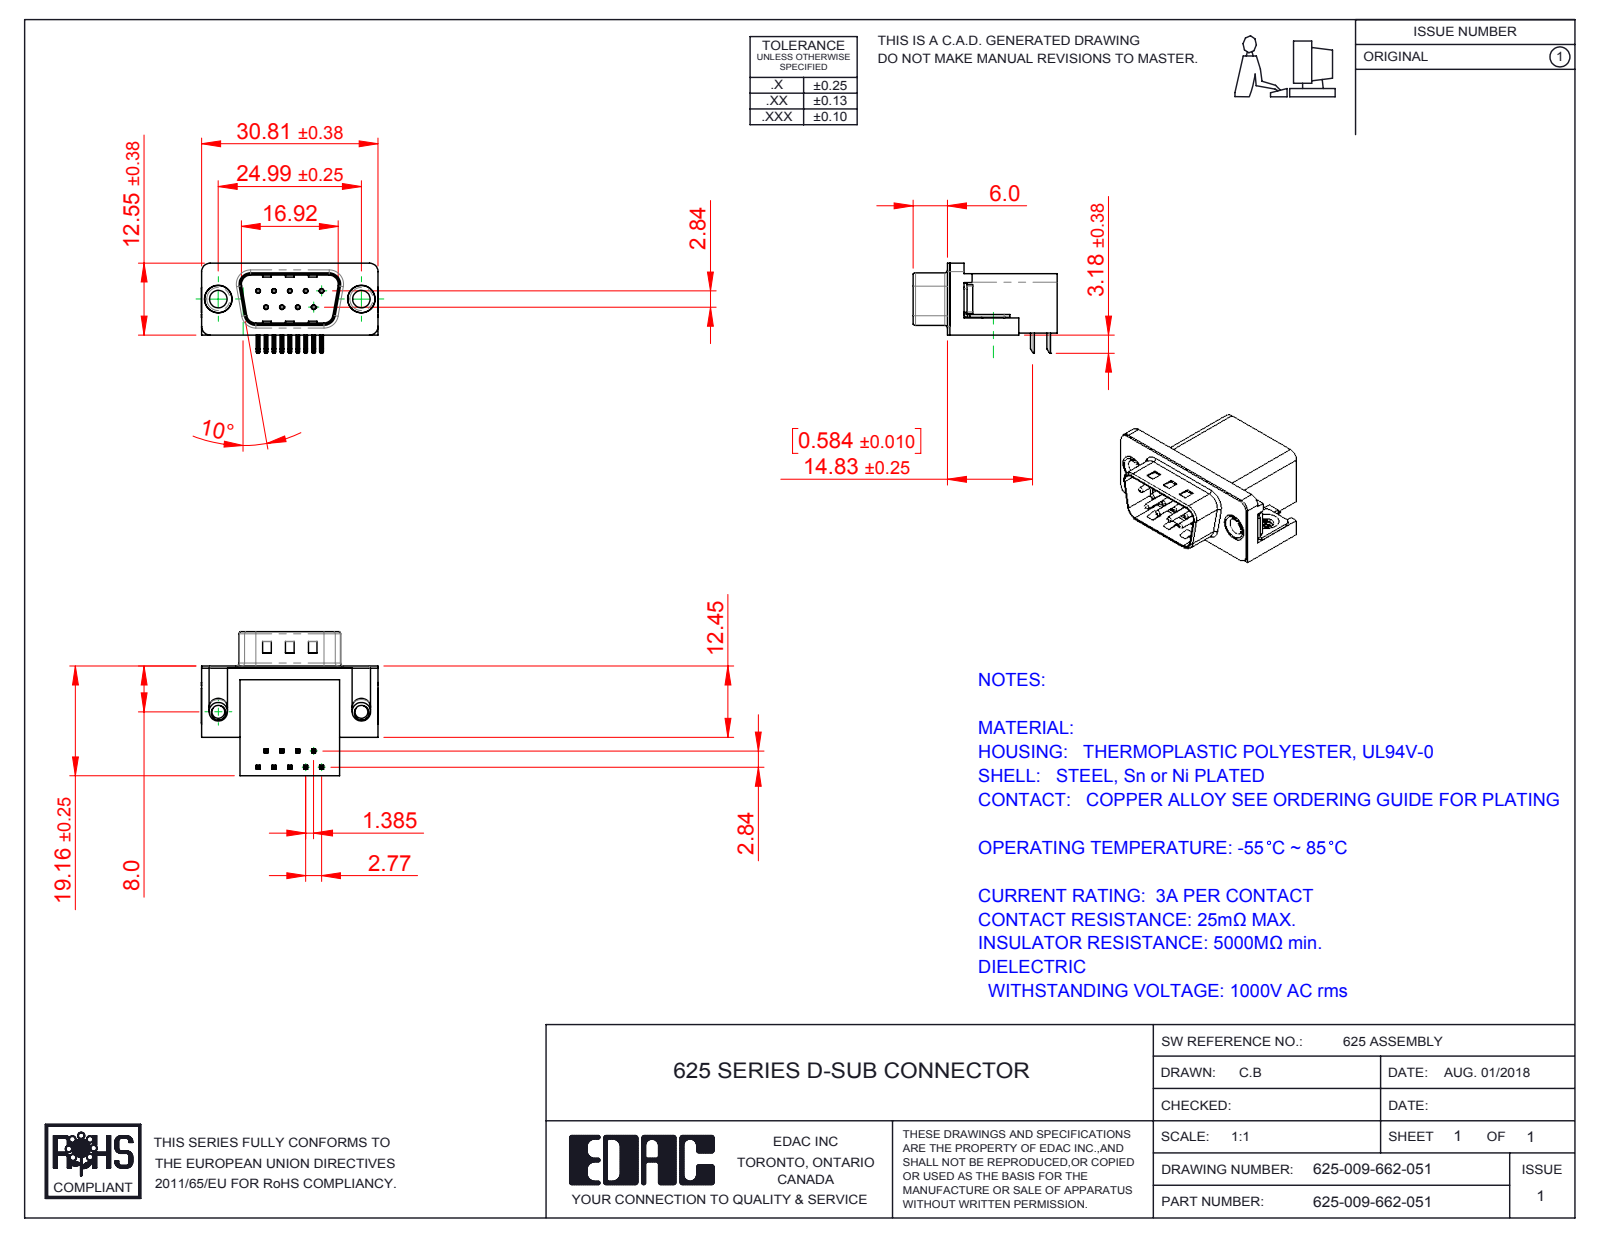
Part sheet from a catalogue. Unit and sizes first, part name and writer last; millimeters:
Units: millimetres
Overall size (bounding box): 30.89 × 25.16 × 15.73
Round holes (diameter × count): ⌀0.35 ×9, ⌀0.8 ×9, ⌀2.26 ×2, ⌀3.05 ×2, ⌀4 ×2, ⌀4.8 ×2, ⌀5 ×2
Round bosses / shafts (diameter × count): ⌀0.75 ×9, ⌀4.9 ×2, ⌀4.75 ×2, ⌀3.85 ×2, ⌀3.26 ×2
Partial cylindrical surfaces — rounded edges, fillets, slot ends (radius × count): R0.25 ×44, R0.12 ×18, R1 ×16, R0.5 ×9, R1.5 ×8, R1.6 ×8, R0.9 ×4, R2 ×4
Main face-to-face distances: 0.4, 10.34, 18.76, 19.16, 2.9, 16.26, 2.5, 0.35, 10.69, 6.7
Hole centre spacings: 3.16, 2.77, 5.54, 5.03, 5.04, 8.31, 7.48, 7.49
Volume: 4 474 mm³ · Surface area: 5 007 mm²
Bodies: 15 solids, 985 faces (575 planar, 311 cylindrical, 99 other)
Part name (STEP PRODUCT): 625 Housing_9 Socket; 625 Thru Hole Rivet; 625 Shell_9 Socket; 625-009-662-051 (+3 more)
STEP written by: SolidWorks 2016 (CONFIG_CONTROL_DESIGN)
